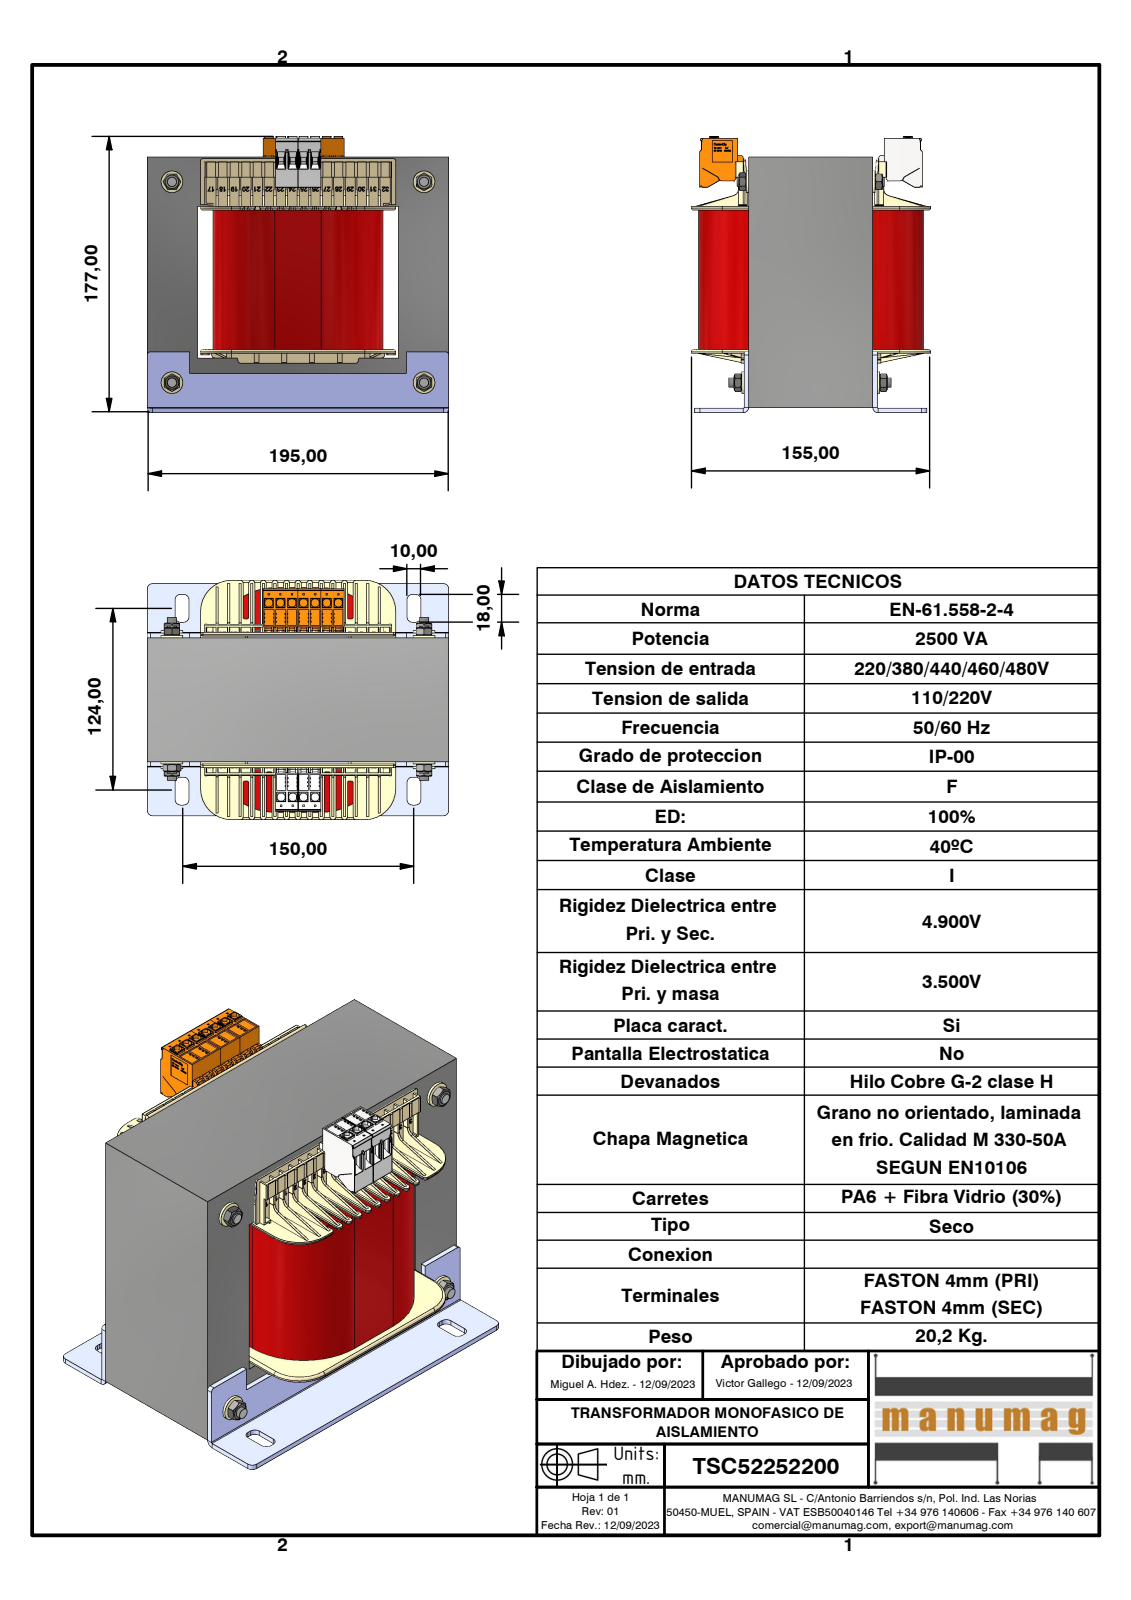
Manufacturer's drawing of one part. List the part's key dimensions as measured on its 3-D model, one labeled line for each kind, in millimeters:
Part name (STEP PRODUCT): TSC52252200; EI195 x 162 - 80 (Rc65); EI192_82_AK_25372_1_Wz837 BOBINADO; EI192_82_AK_25372_1_Wz837 (+8 more)
STEP written by: Autodesk Inventor 2023 (AUTOMOTIVE_DESIGN)
Units: millimetres
Bodies: 30 solids, 11200 faces (8310 planar, 1285 cylindrical, 1605 other)
Overall size (bounding box): 195 × 179 × 154.6
Volume: 3 017 000 mm³ · Surface area: 490 521 mm²
Round holes (diameter × count): ⌀4.92 ×4, ⌀6 ×4, ⌀11 ×4, ⌀9.9 ×2
Round bosses / shafts (diameter × count): ⌀14 ×4, ⌀7.6 ×4
Partial cylindrical surfaces — rounded edges, fillets, slot ends (radius × count): R0.15 ×413, R0.2 ×126, R1 ×52, R1.5 ×44, R0.5 ×42, R1.95 ×22, R3.5 ×22, R0.3 ×12
Main face-to-face distances: 130, 32.5, 80, 162.5, 3, 2.4, 92.6, 65, 32, 97.5
Hole centre spacings: 130, 163, 208.49
